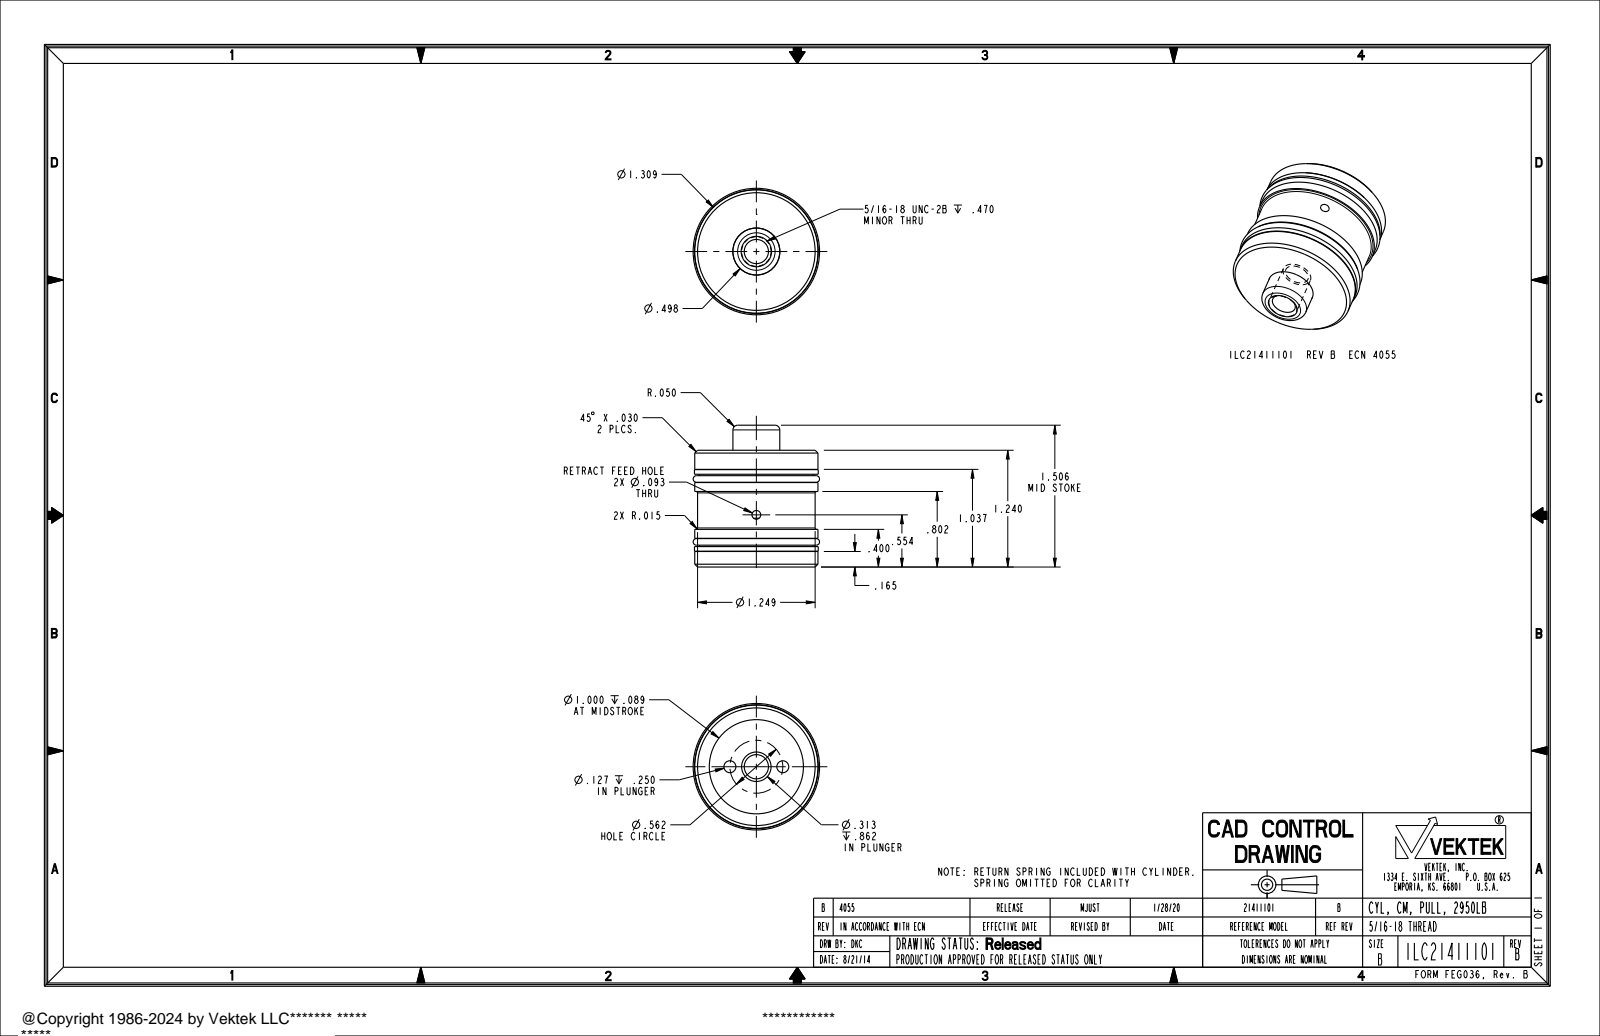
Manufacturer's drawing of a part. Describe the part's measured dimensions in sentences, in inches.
The part is named "ILC21411101_BODY; ILC21411101_PLUNGER; ILC21411101". Its 3-D file was written by "PRO/ENGINEER BY PARAMETRIC TECHNOLOGY CORPORATION, 2017170 (AUTOMOTIVE_DESIGN)". It is 2 solids with 84 faces: 20 planar, 48 cylindrical and 16 other. Overall it measures 1.506 by 1.343 by 1.343 inches. Its volume is 1.437 cubic inches and its surface area 19.5 square inches. Round holes: 2 of diameter 0.127, 1 of diameter 0.093, 1 of diameter 0.257, 1 of diameter 0.313, 1 of diameter 0.5, 1 of diameter 1. Round bosses or shafts: 1 of diameter 1.315, 1 of diameter 1.309, 1 of diameter 1.249, 1 of diameter 1.209, 1 of diameter 0.498. The main face-to-face distances are 0.088, 1.151, 0.634, 0.722, 0.429, 0.517, 0.518, 1.24, 0.606, 0.089. The hole center spacings are 0.281, 0.562.
